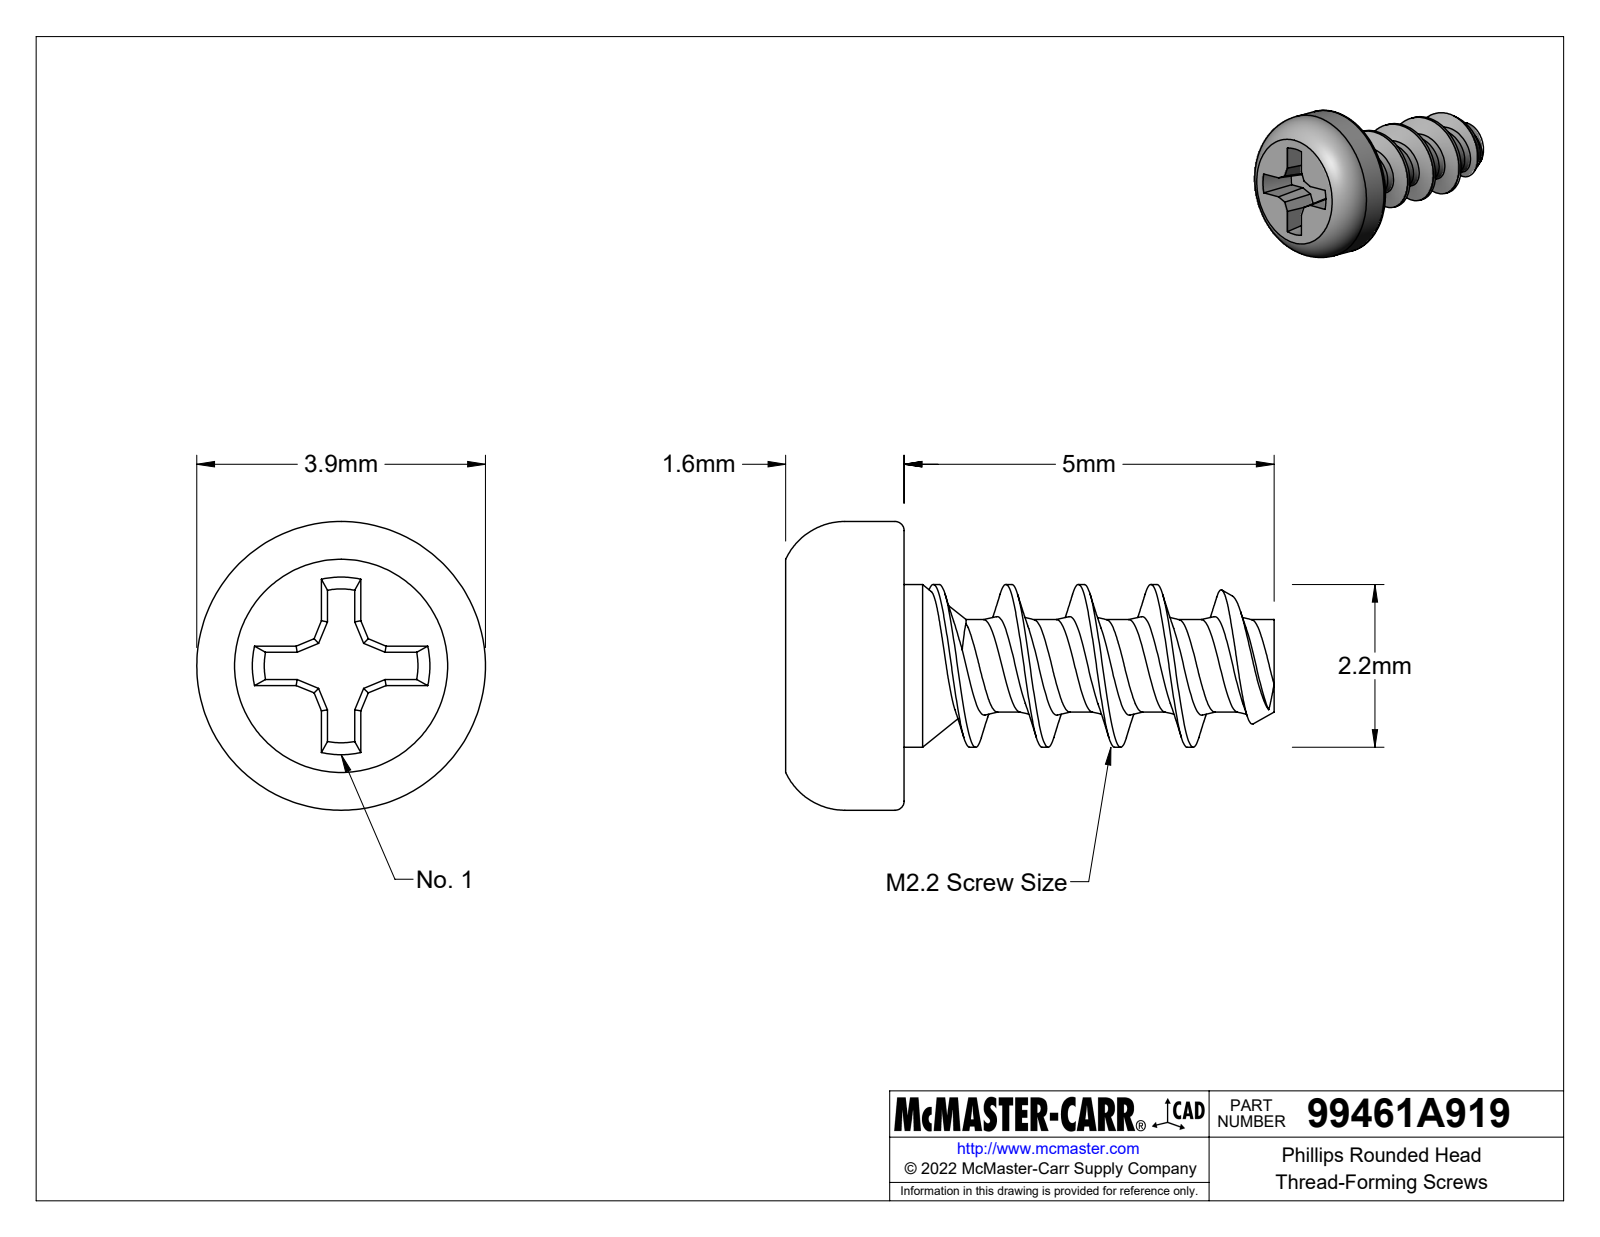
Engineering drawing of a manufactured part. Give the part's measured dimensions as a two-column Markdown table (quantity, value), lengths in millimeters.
| quantity | value |
| --- | --- |
| part name | 99461A919_Phillips Rounded Head Thread-Forming Screws |
| STEP written by | SolidWorks 2017 (CONFIG_CONTROL_DESIGN) |
| units | millimeters |
| bodies | 1 solid, 53 faces (20 planar, 14 cylindrical, 19 other) |
| overall size | 6.6 × 3.9 × 3.9 |
| volume | 26 mm³ |
| surface area | 83 mm² |
| round bosses / shafts (diameter × count) | 3.9 × 1, 2.2 × 1, 1.25 × 1 |
| main face-to-face distances | 1.6, 0.69, 0.91, 5, 5.69, 6.6 |
